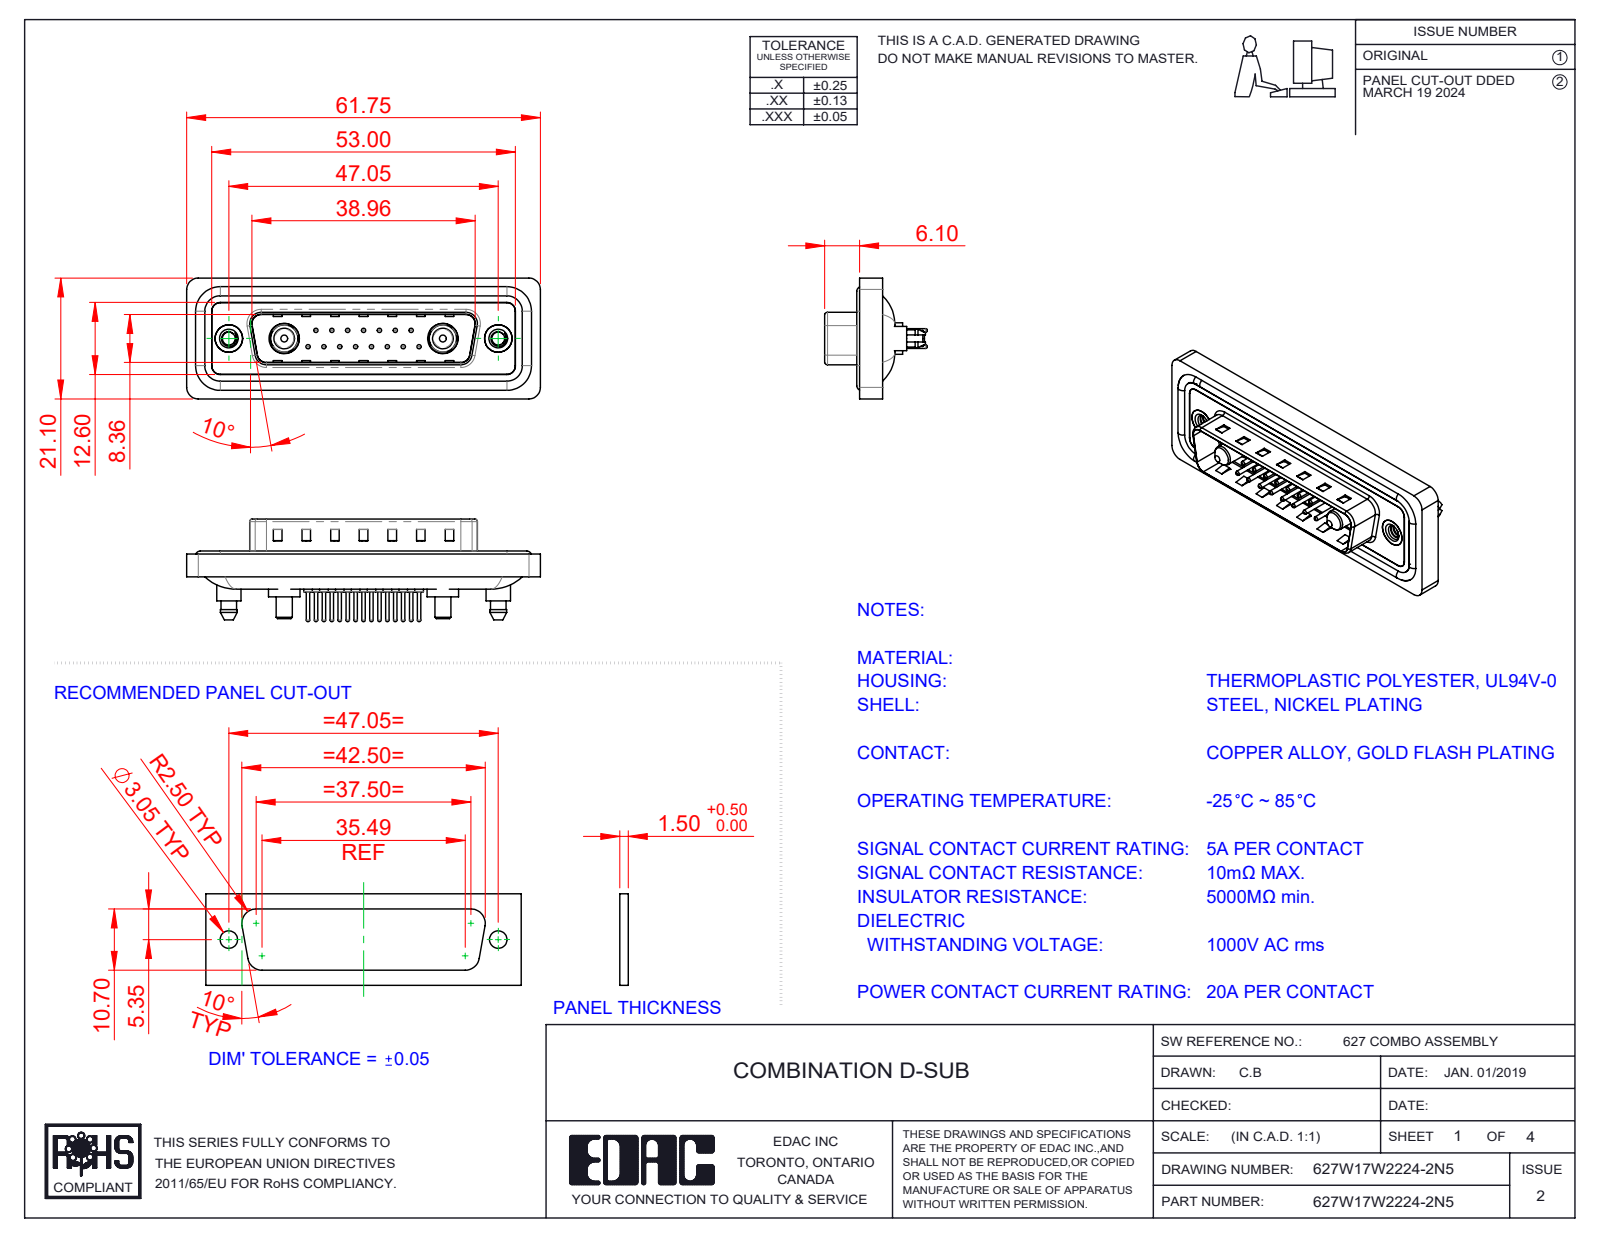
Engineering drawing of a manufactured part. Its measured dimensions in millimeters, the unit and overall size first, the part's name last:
Units: millimetres
Overall size (bounding box): 61.75 × 21.1 × 17.9
Round holes (diameter × count): ⌀0.75 ×15, ⌀1.6 ×15, ⌀2 ×15, ⌀2.26 ×2, ⌀4 ×2, ⌀4.8 ×2, ⌀4.85 ×2, ⌀5 ×2, ⌀5.3 ×2
Round bosses / shafts (diameter × count): ⌀1.5 ×15, ⌀0.6 ×15, ⌀1.6 ×4, ⌀5.5 ×2, ⌀5.4 ×2, ⌀5.2 ×2, ⌀4.9 ×2, ⌀4.75 ×2
Partial cylindrical surfaces — rounded edges, fillets, slot ends (radius × count): R1.5 ×24, R2 ×18, R1.6 ×10, R0.5 ×8, R0.25 ×4, R0.6 ×4, R0.65 ×4, R0.9 ×4
Main face-to-face distances: 0.4, 1.5, 1.1, 1.6, 0.5, 3.1, 2.9, 0.82, 9.58, 4.1
Hole centre spacings: 3.16, 2.77, 5.54, 8.31, 5.04, 7.49, 11.08, 5.03
Volume: 7 400 mm³ · Surface area: 12 247 mm²
Bodies: 26 solids, 1166 faces (350 planar, 468 cylindrical, 348 other)
Part name (STEP PRODUCT): 627Combo Shell Rear_25 Contacts; 627Combo Contact Row 2_24; 627Combo Housing_17W2; 627Combo Shell Front_25 Contacts (+5 more)
STEP written by: SolidWorks 2023 (CONFIG_CONTROL_DESIGN)
